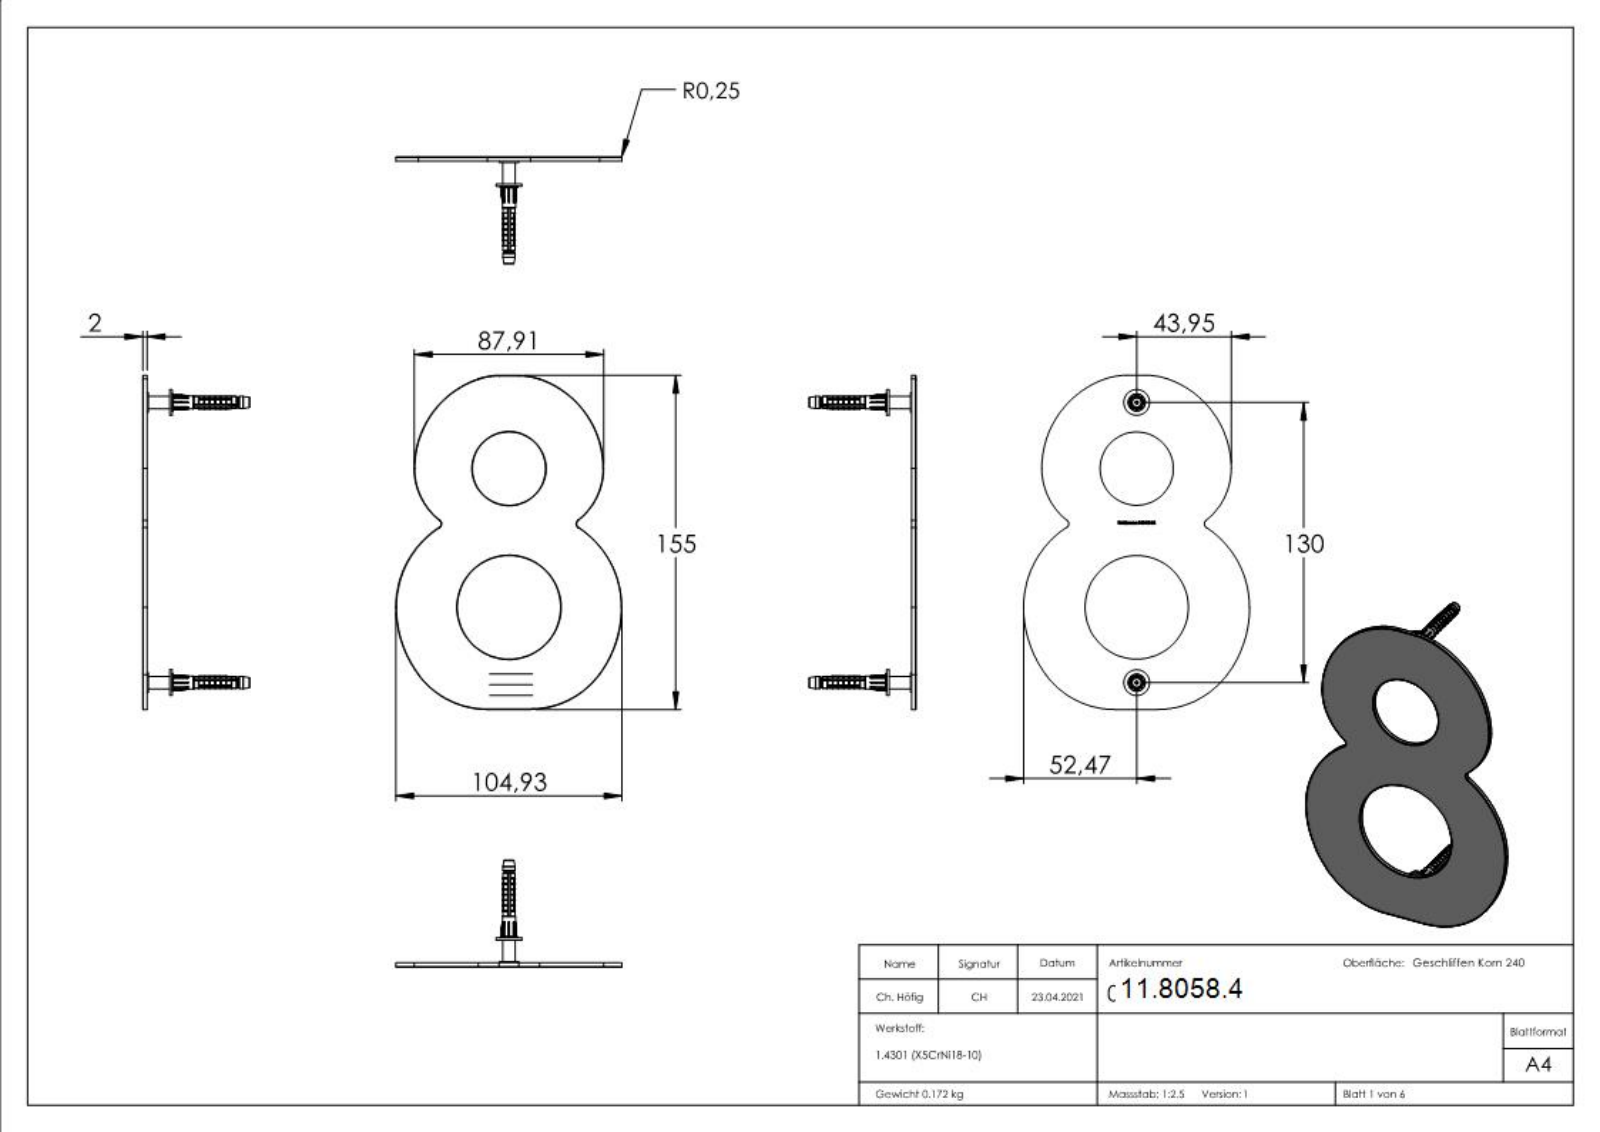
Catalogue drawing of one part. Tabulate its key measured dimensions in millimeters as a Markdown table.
| quantity | value |
| --- | --- |
| part name | 040-HN-X Teil3_040-HN-X Teil3; 040-HN-X Teil1_040-HN-8 Teil1; 040-HN-X Teil4; 040-HN-X Teil3 (+5 more) |
| STEP written by | SolidWorks 2018 (CONFIG_CONTROL_DESIGN) |
| units | millimeters |
| bodies | 7 solids, 1582 faces (355 planar, 399 cylindrical, 828 other) |
| overall size | 10000 × 5217.43 × 4607.88 |
| volume | 22 739 mm³ |
| surface area | 25 816 mm² |
| round holes (diameter × count) | 3.3 × 2, 4.3 × 2, 34 × 1, 48 × 1 |
| round bosses / shafts (diameter × count) | 12 × 2, 9 × 2, 8 × 2, 6 × 2, 5.8 × 2, 5.6 × 2, 4.6 × 2, 4 × 2 |
| partial cylindrical surfaces (radius × count) | 0.1 × 22, 0.25 × 2, 2 × 2, 3.5 × 2, 30 × 2, 30.67 × 2, 40 × 2, 44.18 × 2 |
| main face-to-face distances | 2, 11.6, 13.6, 1.1, 10.5, 12.5, 0.5, 2.5, 10, 11.1 |
| hole center spacings | 30.7, 34.95, 64.35, 95.05, 99.3, 130 |
